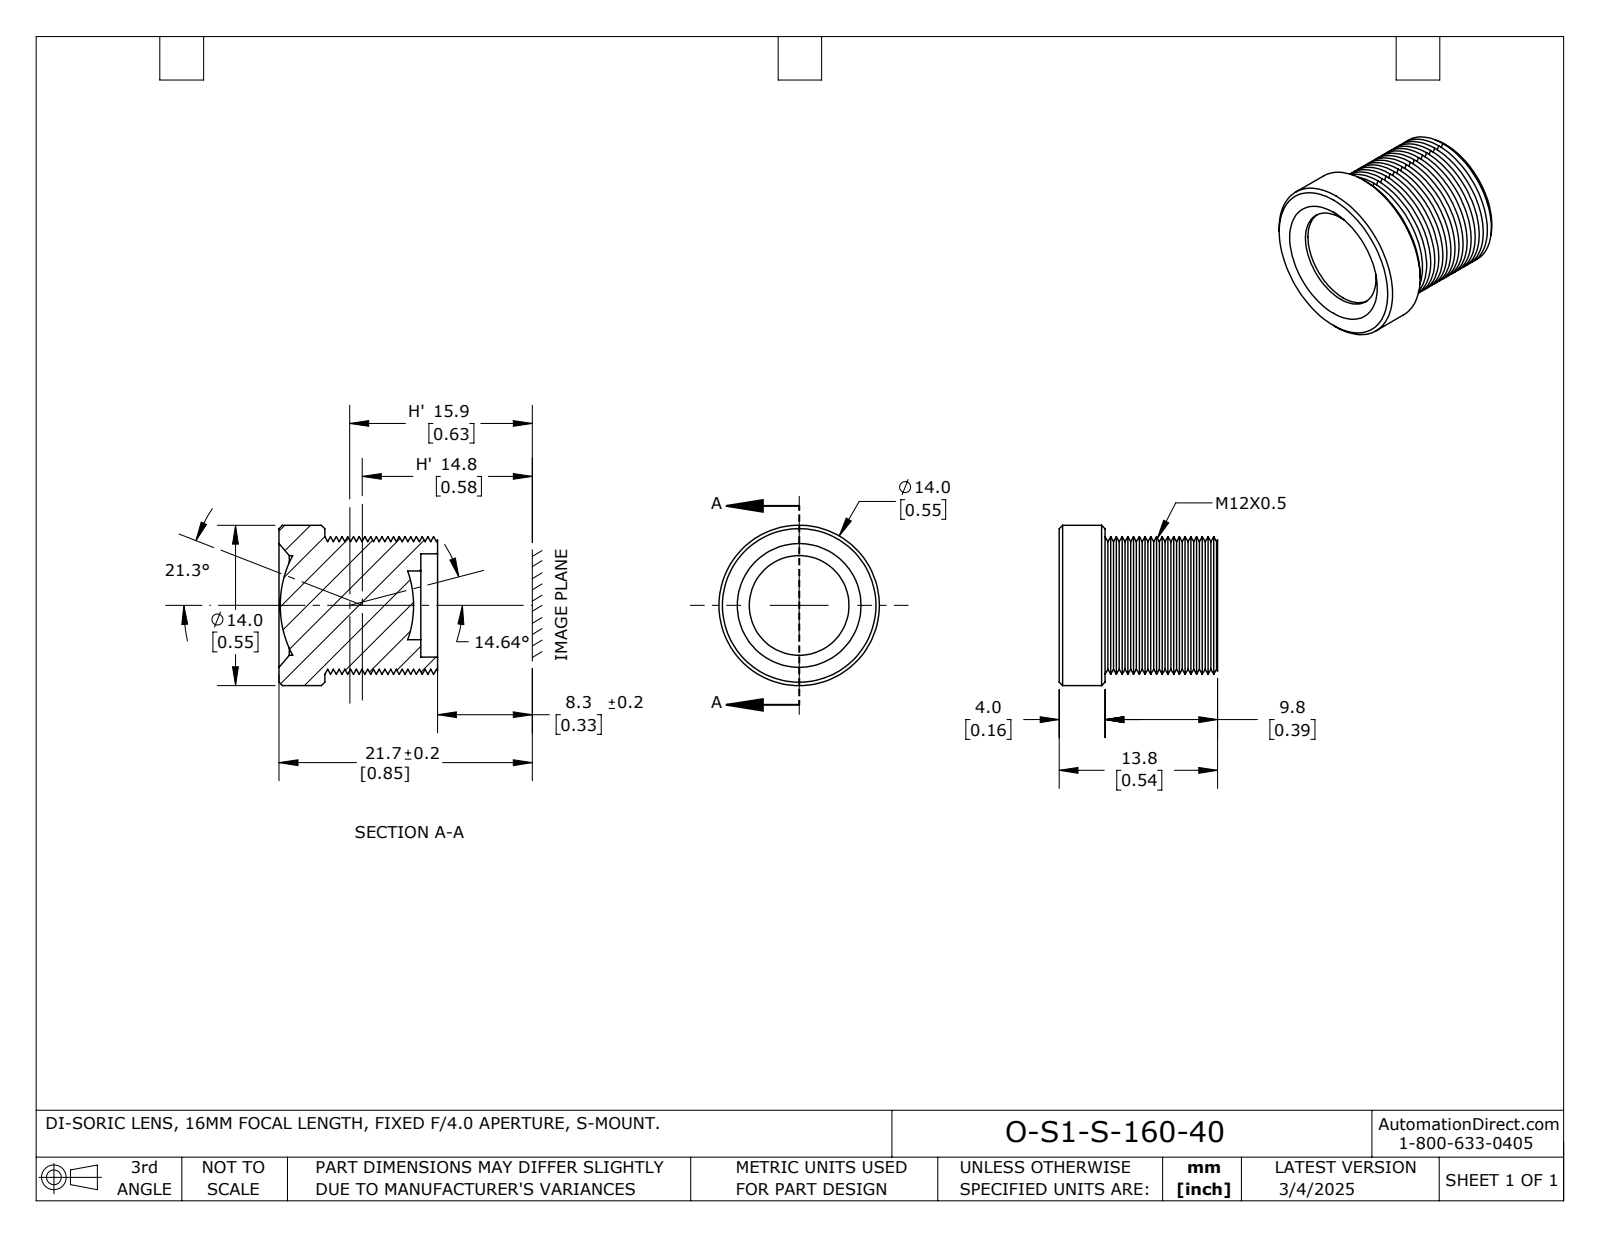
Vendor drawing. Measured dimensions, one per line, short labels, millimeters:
name: O-S1-S-160-40 -- 213098
written by: SolidWorks 2024 (AUTOMOTIVE_DESIGN)
unit: mm
bodies: 1 solid, 102 faces (4 planar, 8 cylindrical, 90 other)
size: 14 × 14 × 13.84
volume: 1 476 mm³; area: 1 258 mm²
holes: 1× ⌀6, 1× ⌀8.7, 1× ⌀9
bosses: 1× ⌀14
face distances: 13.84, 12.39, 1.45, 4, 8.39, 9.84
